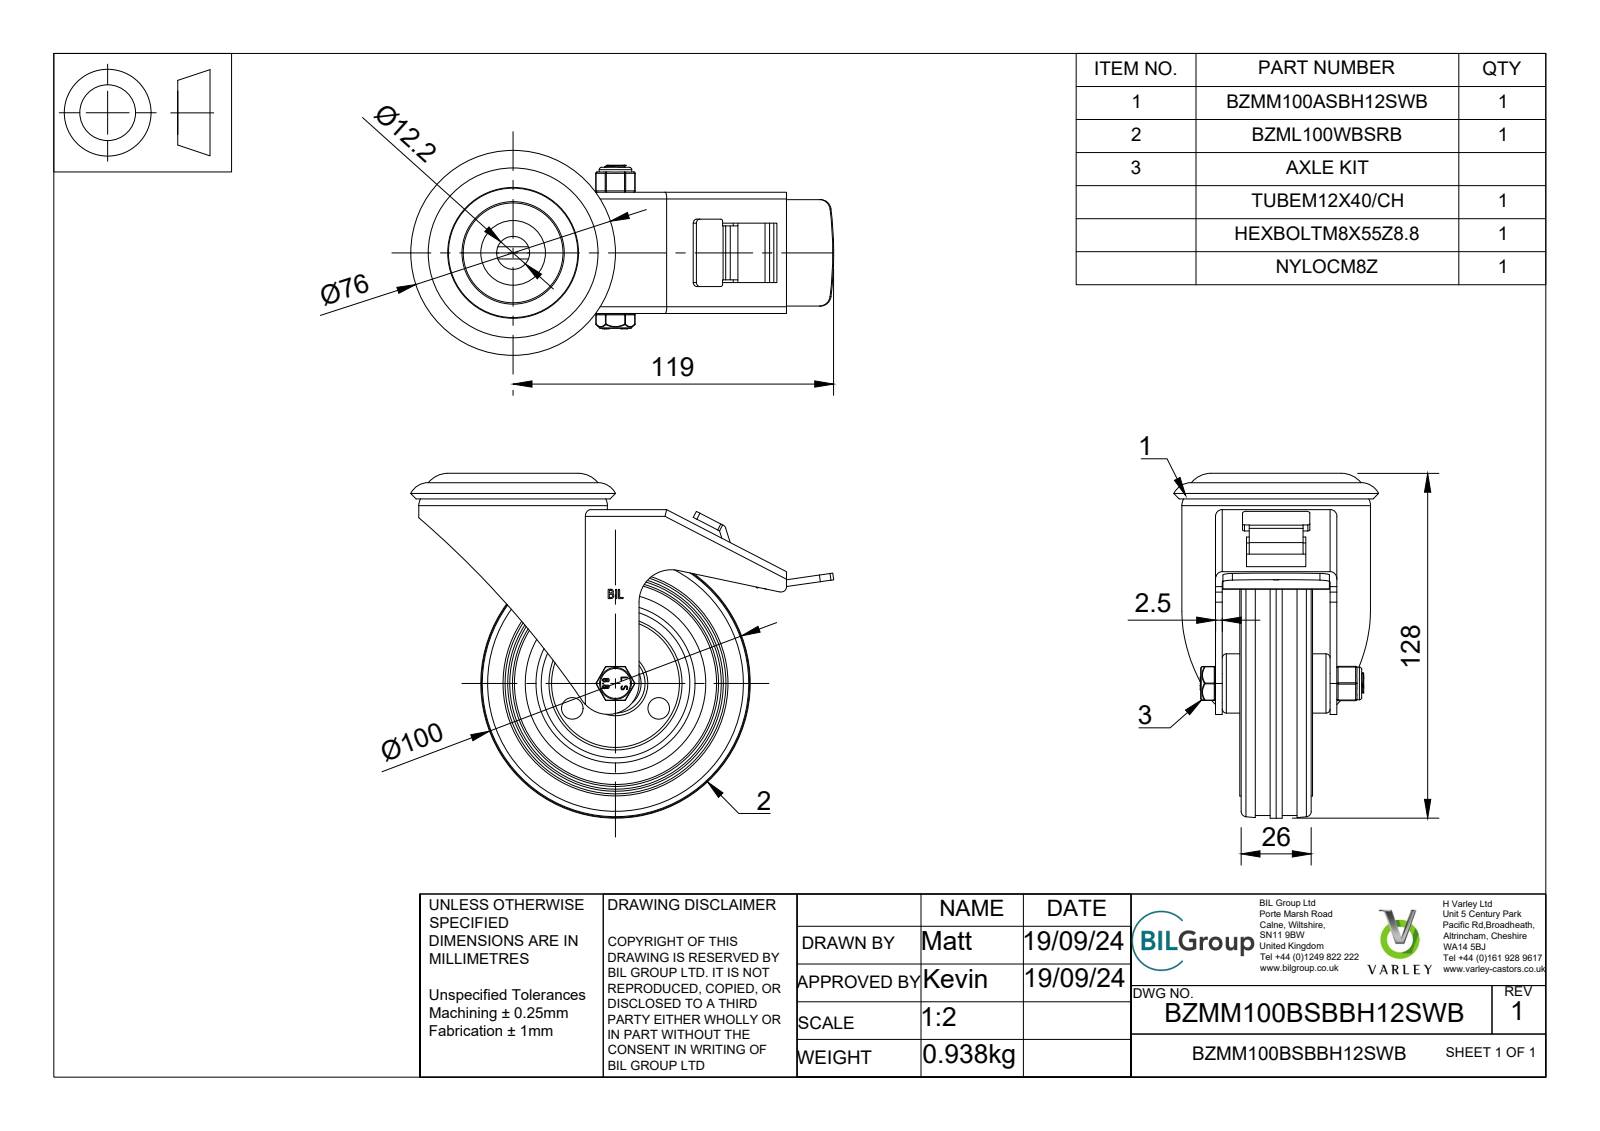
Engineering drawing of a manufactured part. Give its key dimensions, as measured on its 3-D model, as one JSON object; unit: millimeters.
{"part_name": "BZMM100BSBBH12SWB v3; BZMM100ASBH12SWB v1; PRESSED STEEL, ZINC PLATED HEAD; PRESSED STEEL, ZINC PLATED FORKS (+7 more)", "step_written_by": "Autodesk Translation Framework v13.20.0.188 (AUTOMOTIVE_DESIGN)", "units": "millimeters", "bodies": {"solids": 22, "faces": 746, "planar": 373, "cylindrical": 254, "other": 119}, "overall_size": [157, 128, 76], "volume_mm3": 234336, "surface_area_mm2": 122130, "round_holes": [[5, 3], [0.66, 2], [12.2, 2], [8, 1], [8.2, 1], [8.4, 1], [8.6, 1], [12.5, 1], [20, 1], [50.93, 1], [65, 1], [67, 1]], "round_bosses_or_shafts": [[3.5, 8], [8, 3], [100, 1], [98, 1], [83.5, 1], [80, 1], [76.5, 1], [70, 1]], "partial_cylinders_radius": [[0.75, 50], [0.5, 18], [0.25, 12], [1.25, 10], [0.33, 4], [0.64, 4], [2.5, 4], [2, 3]], "face_to_face_distances": [2.5, 0.5, 7, 26, 9.5, 1, 6.5, 33, 35.5, 42.5], "hole_center_spacings": [18.5, 32.04, 3.22, 2.49, 15.31, 16.75, 17.5, 19.96]}
